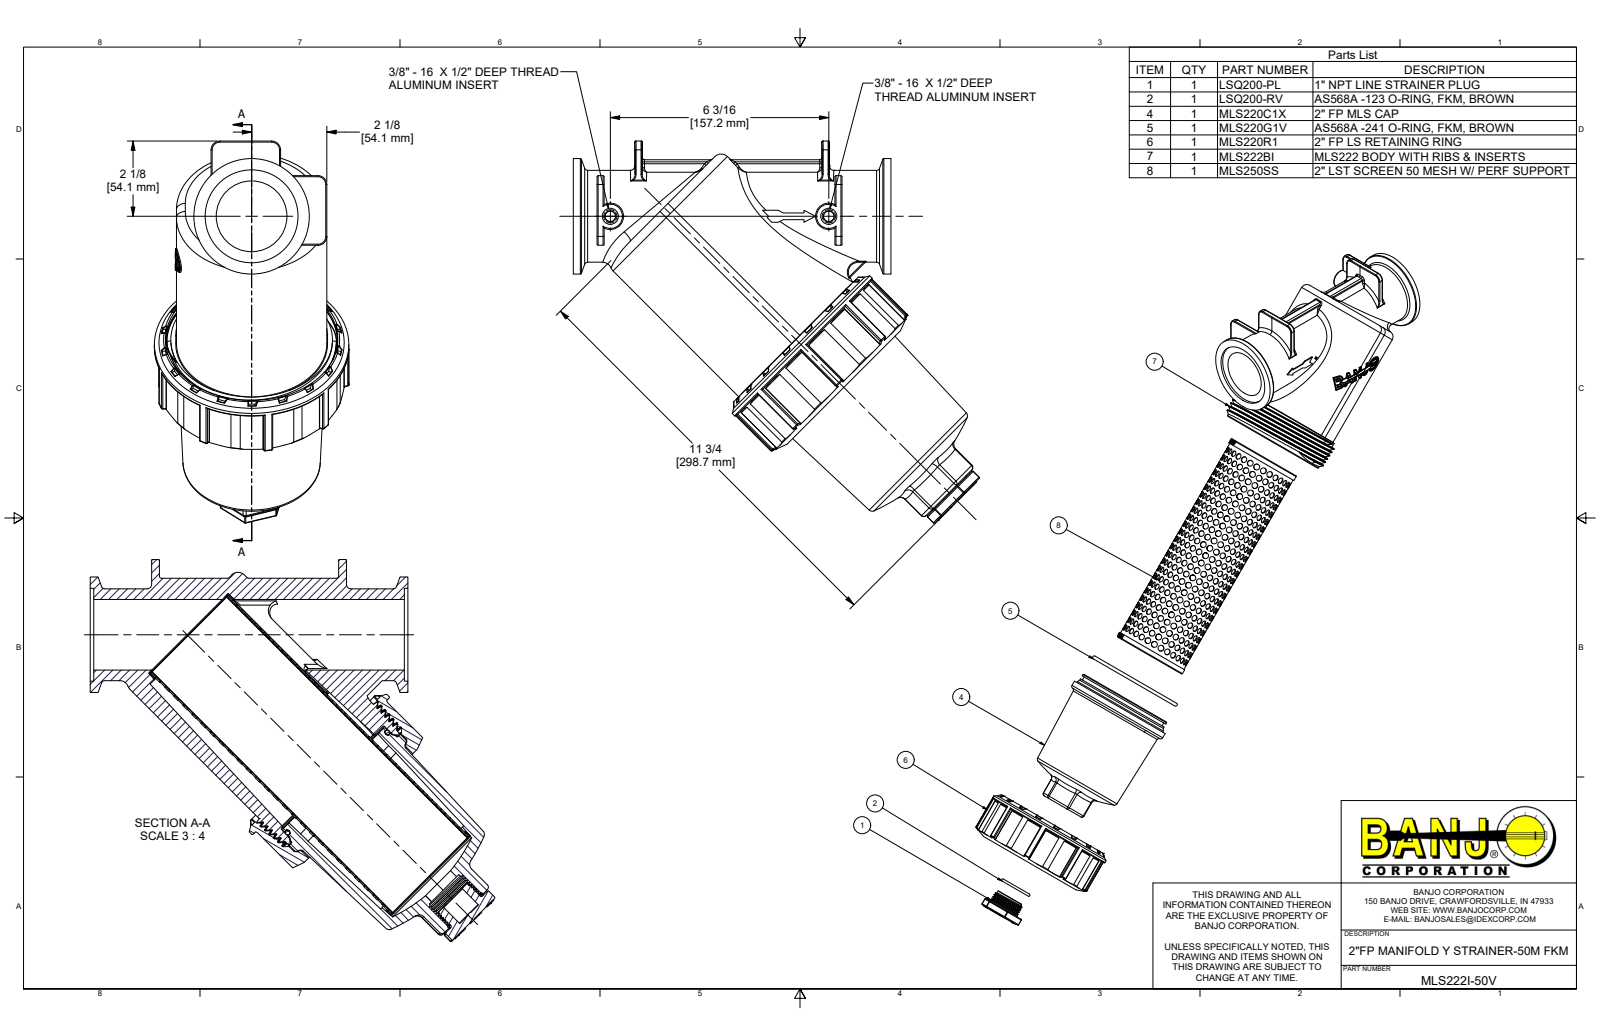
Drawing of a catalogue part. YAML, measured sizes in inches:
part_name: "MLS222I-50V; MLS222BI; MLS222B; V25022 (+7 more)"
step_written_by: "Autodesk Inventor 2022 (AUTOMOTIVE_DESIGN)"
units: inches
bodies: {solids: 13, faces: 2818, planar: 852, cylindrical: 1128, other: 838}
overall_size: [11.507, 10.817, 5.51]
volume: 85
surface_area: 887.4
round_holes:
  - {diameter: 0.25, count: 723}
  - {diameter: 0.295, count: 2}
  - {diameter: 0.307, count: 2}
  - {diameter: 2.937, count: 2}
  - {diameter: 3.128, count: 2}
  - {diameter: 0.454, count: 1}
  - {diameter: 0.641, count: 1}
  - {diameter: 0.75, count: 1}
  - {diameter: 1, count: 1}
  - {diameter: 1.176, count: 1}
  - {diameter: 2, count: 1}
  - {diameter: 2.63, count: 1}
round_bosses_or_shafts:
  - {diameter: 3.188, count: 2}
  - {diameter: 0.5, count: 2}
  - {diameter: 0.455, count: 2}
  - {diameter: 5.51, count: 1}
  - {diameter: 5.25, count: 1}
  - {diameter: 4.45, count: 1}
  - {diameter: 4.215, count: 1}
  - {diameter: 4.1, count: 1}
partial_cylinders:
  - {radius: 0.03, count: 80}
  - {radius: 0.01, count: 36}
  - {radius: 0.06, count: 12}
  - {radius: 0.09, count: 12}
  - {radius: 0.25, count: 8}
  - {radius: 0.125, count: 6}
  - {radius: 0.02, count: 2}
  - {radius: 0.039, count: 2}
face_to_face_distances: [0.1, 8.9, 0.3, 9, 5.809, 6.109, 5.3, 0.03, 0.2, 6.74]
hole_center_spacings: [0.363, 1.45, 0.725, 2.537, 3.263, 1.087, 2.175, 4.35]
